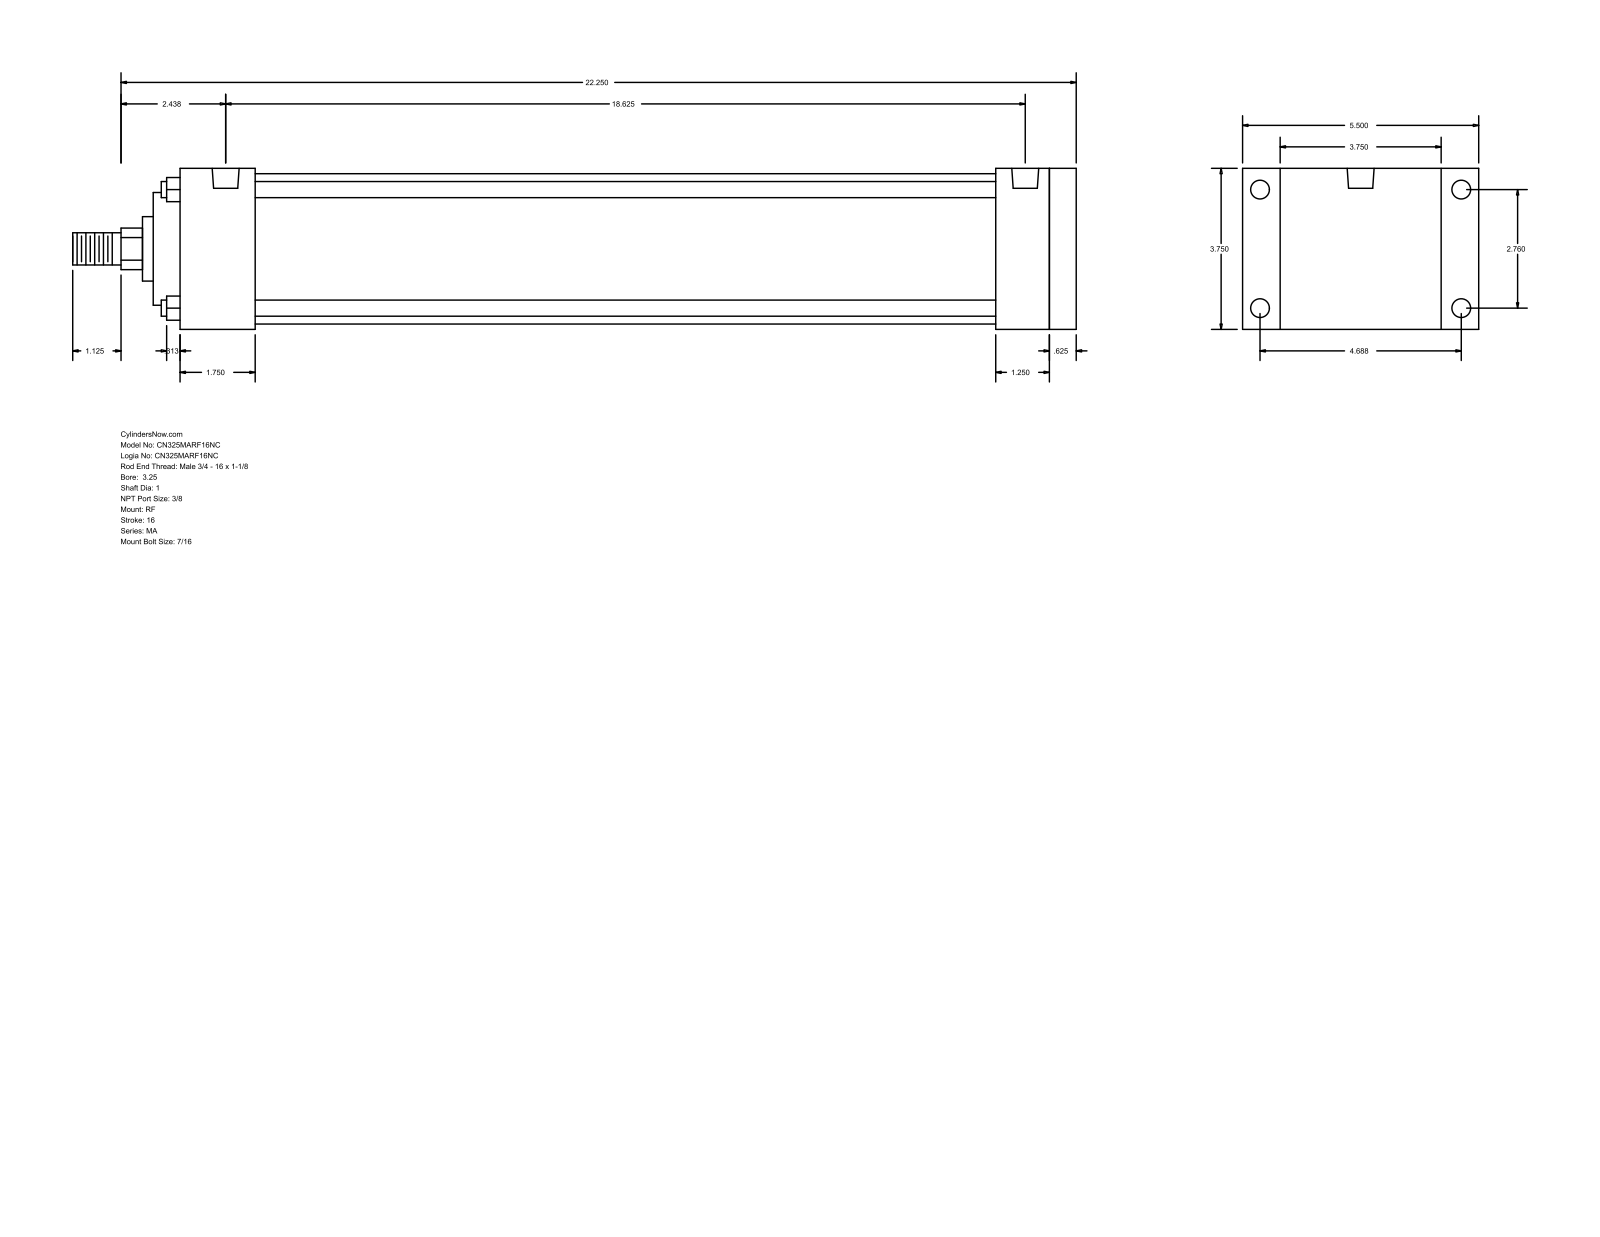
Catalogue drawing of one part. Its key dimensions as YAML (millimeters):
part_name: "MA_RF__0325_1"
step_written_by: "GSSL Pune (CONFIG_CONTROL_DESIGN)"
units: millimeters
bodies: {solids: 0, faces: 94, planar: 65, cylindrical: 29, other: 0}
overall_size: [593.73, 139.7, 95.25]
round_holes:
  - {diameter: 11.11, count: 8}
  - {diameter: 15.93, count: 2}
round_bosses_or_shafts:
  - {diameter: 9.53, count: 4}
  - {diameter: 88.9, count: 1}
  - {diameter: 66.67, count: 1}
  - {diameter: 38.1, count: 1}
  - {diameter: 25.4, count: 1}
  - {diameter: 19.05, count: 1}
partial_cylinders:
  - {radius: 12.29, count: 1}
face_to_face_distances: [95.24, 530.23, 514.35, 15.88, 22.23, 117.47, 482.6, 31.75, 47.63, 44.46]
hole_center_spacings: [4.76, 70.1, 119.06, 138.16, 463.56, 468.32, 473.08]
